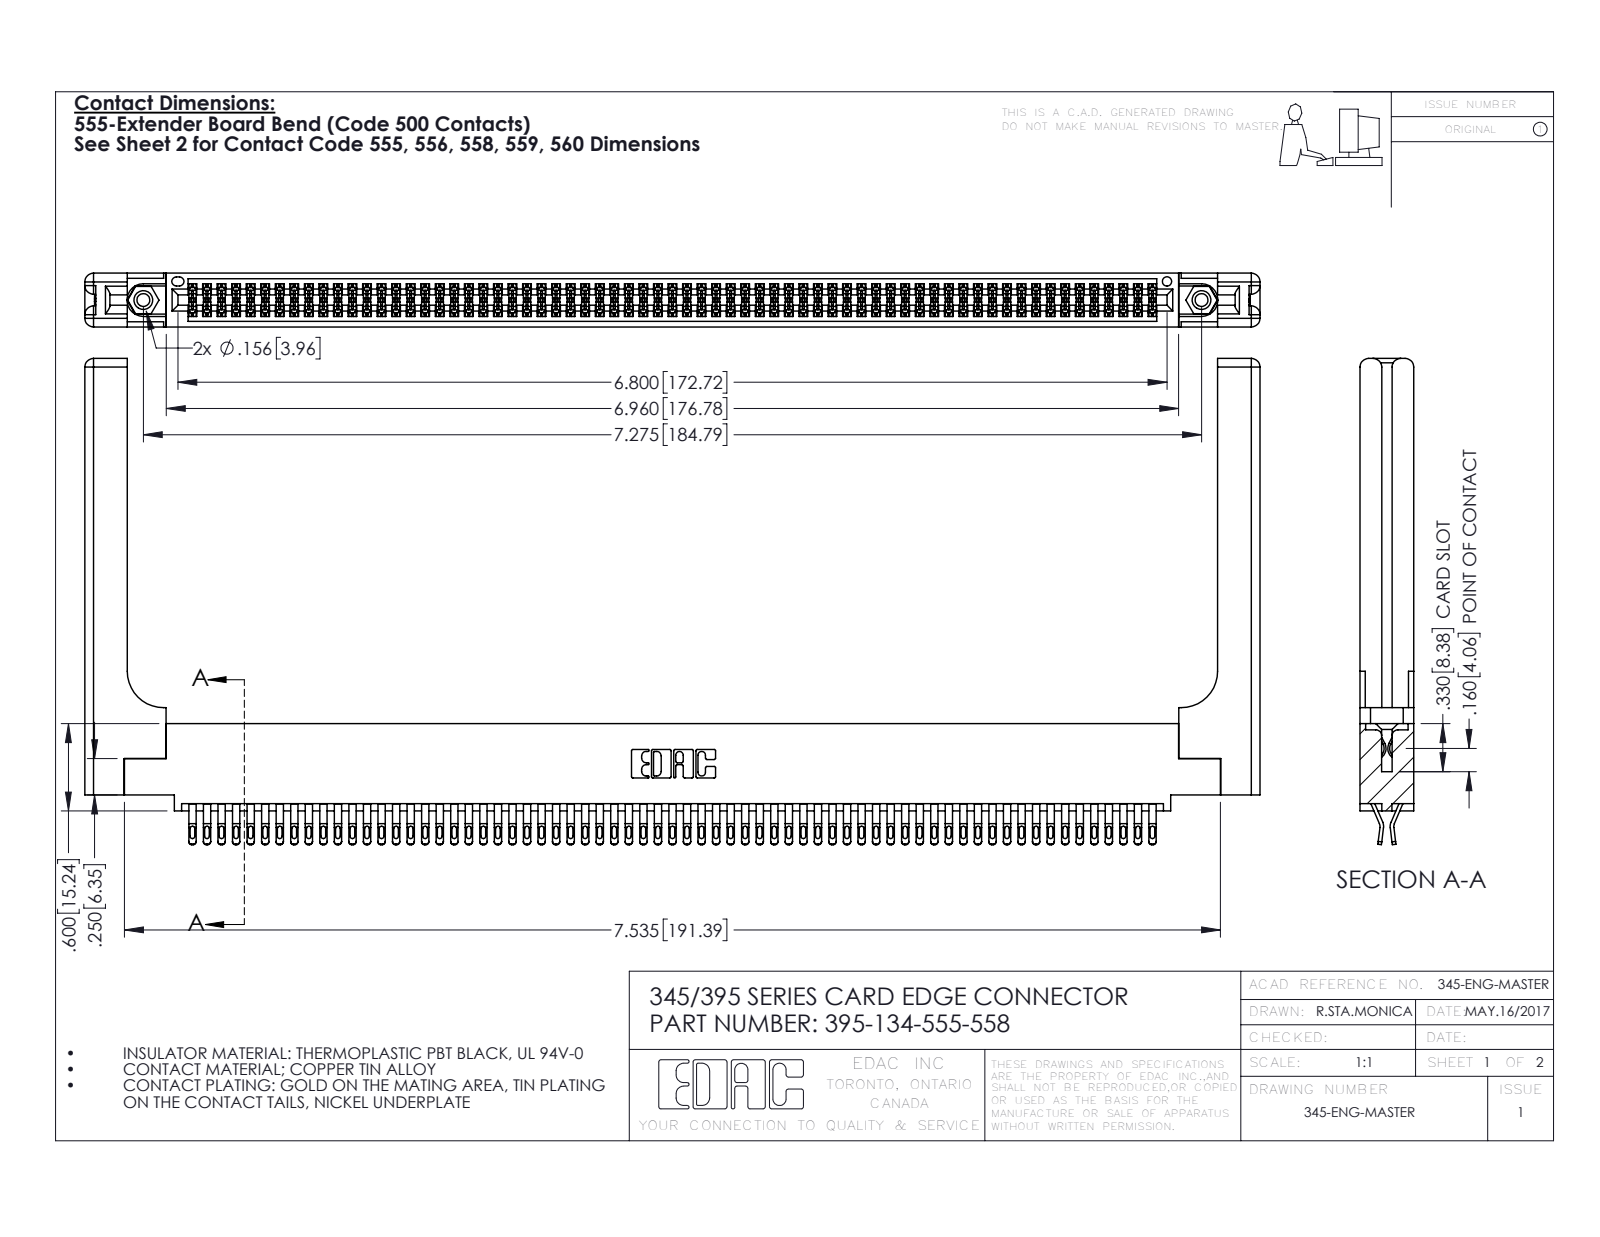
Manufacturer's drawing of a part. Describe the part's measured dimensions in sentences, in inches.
The part is named "345 Part_0.110 Offset - 0.156 Dia-TH; 395-134-555-558; 345-220-058_345-220-058; 345-292-001_555 Tail (+1 more)". Its 3-D file was written by "SolidWorks 2016 (CONFIG_CONTROL_DESIGN)". It is 139 solids with 7890 faces: 4386 planar, 3444 cylindrical and 60 other. Overall it measures 8.079 by 3.342 by 0.37 inches. Its volume is 1.767 cubic inches and its surface area 57.76 square inches. Round holes: 2 of diameter 0.089, 2 of diameter 0.125, 2 of diameter 0.156, 1 of diameter 0.064. Round bosses or shafts: 2 of diameter 0.155. Partial cylindrical surfaces (rounded edges, fillets, slot ends): 335 of radius 0.016, 268 of radius 0.02, 201 of radius 0.006, 22 of radius 0.01, 16 of radius 0.06, 6 of radius 0.007, 6 of radius 0.031, 3 of radius 0.026. The main face-to-face distances are 0.072, 0.298, 0.37, 0.025, 0.098, 0.272, 0.2, 0.225, 0.148, 0.15. The hole center spacings are 0.27, 7.039, 7.275.
